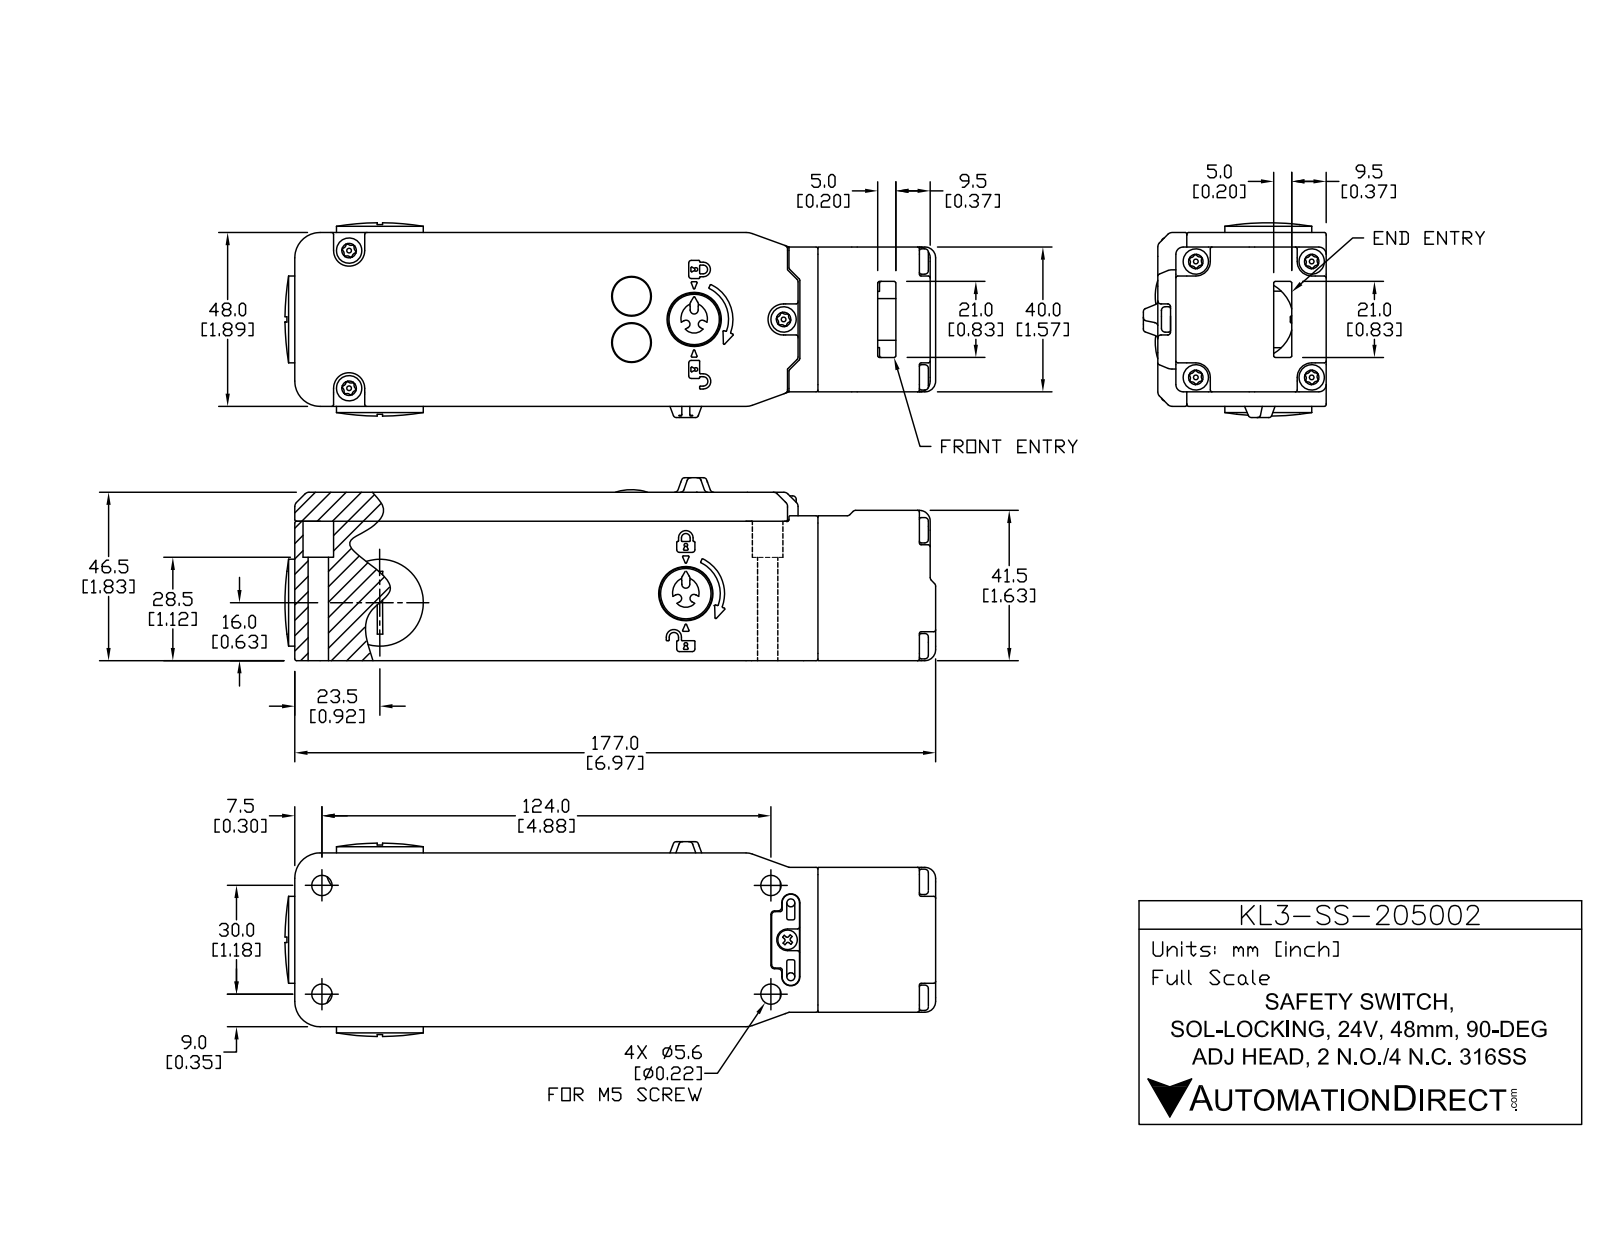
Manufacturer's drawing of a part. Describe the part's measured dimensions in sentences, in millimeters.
The part is named "KL3-SS-205002". Its 3-D file was written by "SolidWorks 2017 (AUTOMOTIVE_DESIGN)". It is 19 solids with 3255 faces: 757 planar, 1350 cylindrical and 1148 other. Overall it measures 179.7 by 53.8 by 50.5 millimeters. Its volume is 132 300 cubic millimeters and its surface area 91 290 square millimeters. Round holes: 7 of diameter 4, 6 of diameter 3, 4 of diameter 4.2, 4 of diameter 5, 4 of diameter 5.6, 4 of diameter 9, 3 of diameter 4.5, 2 of diameter 2.2, 2 of diameter 3.6, 2 of diameter 6.8, 2 of diameter 8.1, 2 of diameter 9.1. Round bosses or shafts: 7 of diameter 7, 7 of diameter 3.5, 7 of diameter 1.3, 4 of diameter 1, 3 of diameter 6, 2 of diameter 24, 2 of diameter 18, 2 of diameter 11.4. Partial cylindrical surfaces (rounded edges, fillets, slot ends): 405 of radius 0.5, 119 of radius 0.2, 105 of radius 1, 41 of radius 0.3, 29 of radius 0.4, 25 of radius 1.5, 20 of radius 0.8, 14 of radius 0.2. The main face-to-face distances are 3.3, 2.2, 44.7, 46.5, 48, 38.5, 44.3, 42, 4, 40.7. The hole center spacings are 22.6, 32, 34, 4.2, 4.6, 6.7, 7, 7.3.
